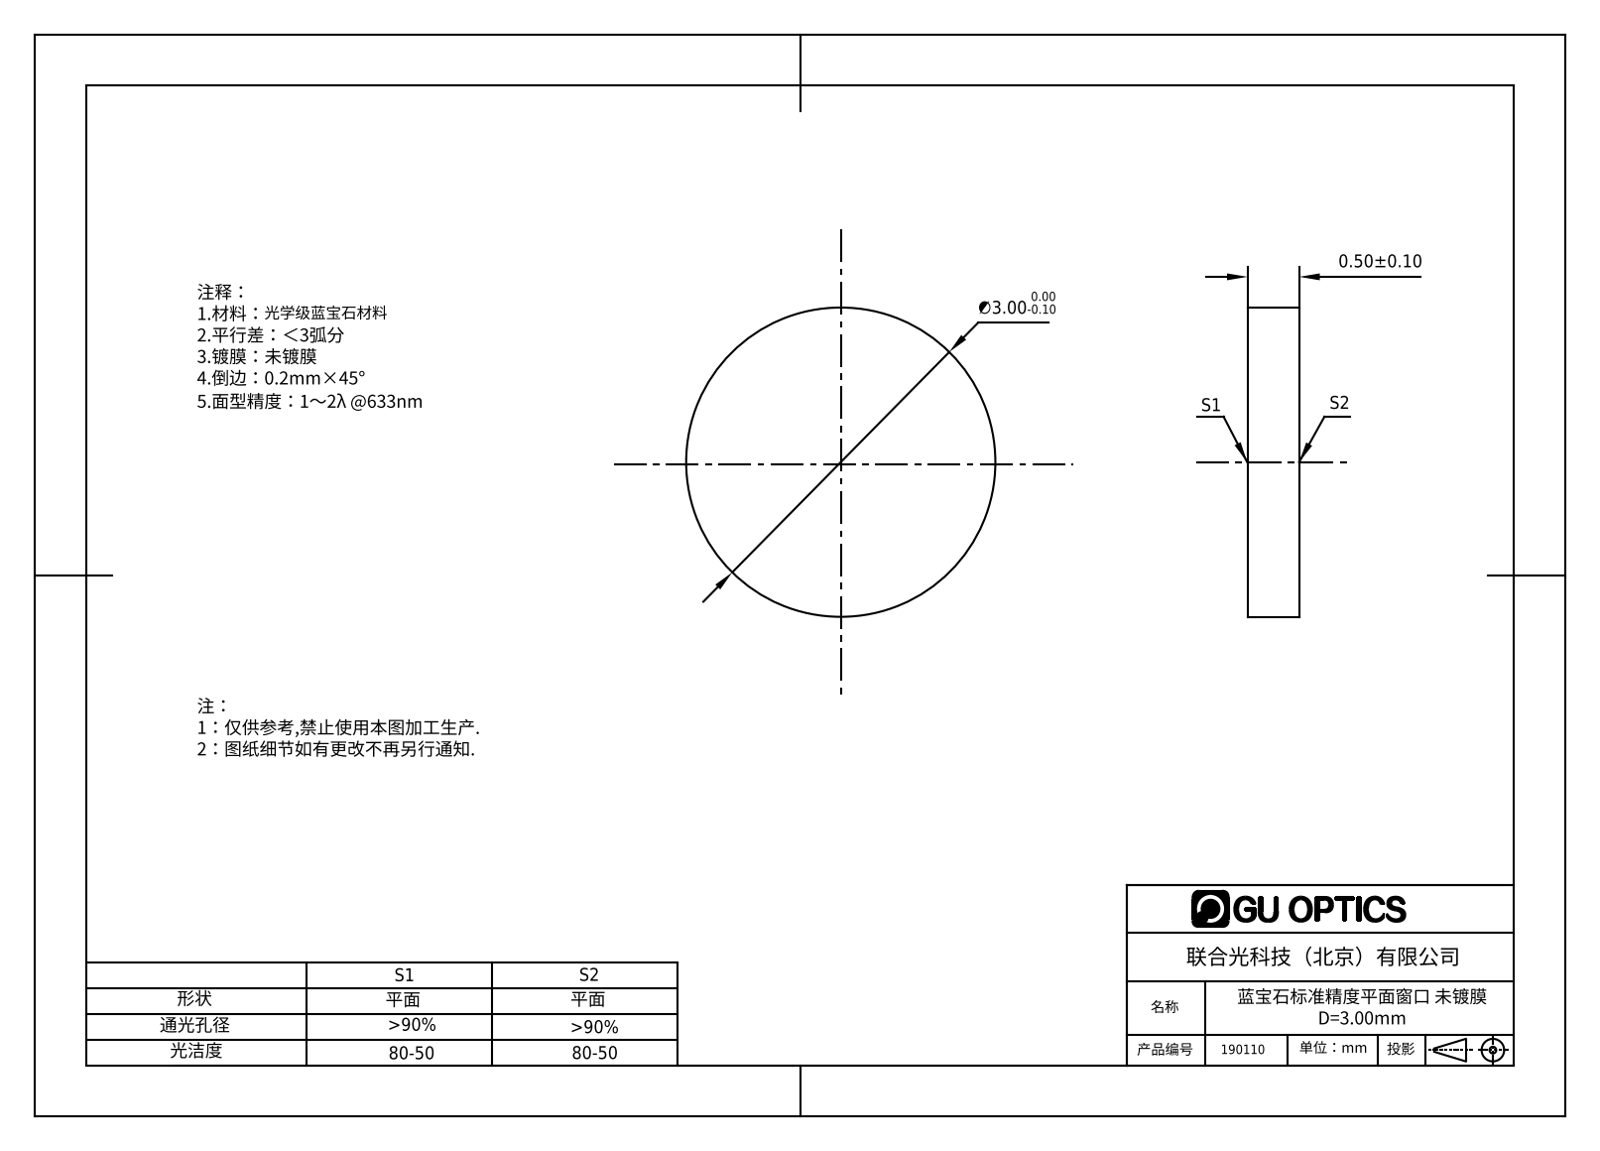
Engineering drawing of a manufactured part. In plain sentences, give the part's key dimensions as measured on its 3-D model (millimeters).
The part is named "190110". Its 3-D file was written by "SolidWorks 2016 (AUTOMOTIVE_DESIGN)". It is 1 solid with 4 faces: 2 planar, 2 cylindrical and 0 other. Overall it measures 3 by 3 by 0.5 millimeters. Its volume is 4 cubic millimeters and its surface area 19 square millimeters. Round bosses or shafts: 1 of diameter 3. The main face-to-face distances are 0.5.
